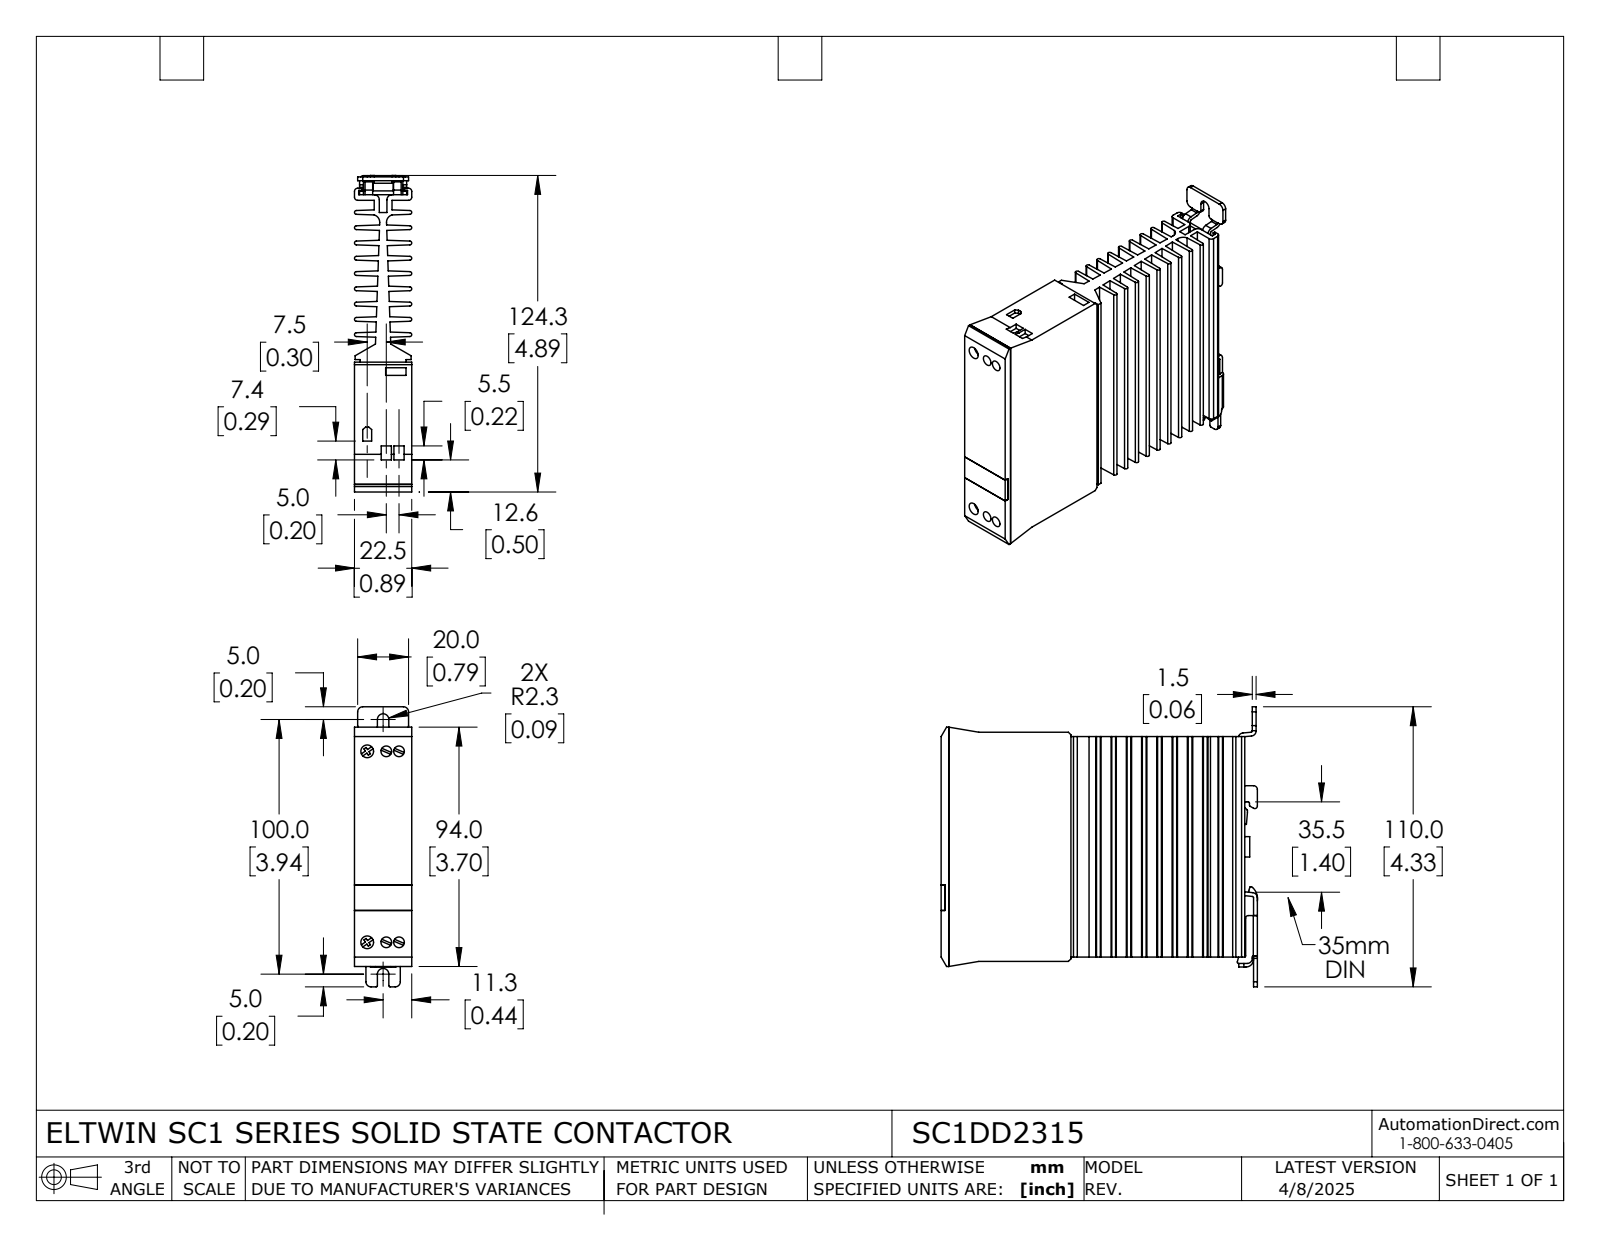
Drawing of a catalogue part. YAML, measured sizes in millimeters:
part_name: "SC1DD2315"
step_written_by: "SolidWorks 2021 (AUTOMOTIVE_DESIGN)"
units: millimeters
bodies: {solids: 6, faces: 489, planar: 326, cylindrical: 161, other: 2}
overall_size: [124.3, 110, 22.5]
volume: 166200
surface_area: 74450
round_holes:
  - {diameter: 4.2, count: 4}
  - {diameter: 4.4, count: 4}
  - {diameter: 5, count: 2}
  - {diameter: 6, count: 2}
round_bosses_or_shafts:
  - {diameter: 8, count: 1}
partial_cylinders:
  - {radius: 0.5, count: 29}
  - {radius: 0.8, count: 18}
  - {radius: 2, count: 18}
  - {radius: 1, count: 15}
  - {radius: 1.5, count: 5}
  - {radius: 1.2, count: 4}
  - {radius: 3, count: 3}
  - {radius: 0.1, count: 2}
face_to_face_distances: [6, 12, 18, 3.8, 14.2, 6, 30, 2.2, 15.7, 8.2]
hole_center_spacings: [75, 5, 7.5, 12.5, 75.2, 75.4, 76]
